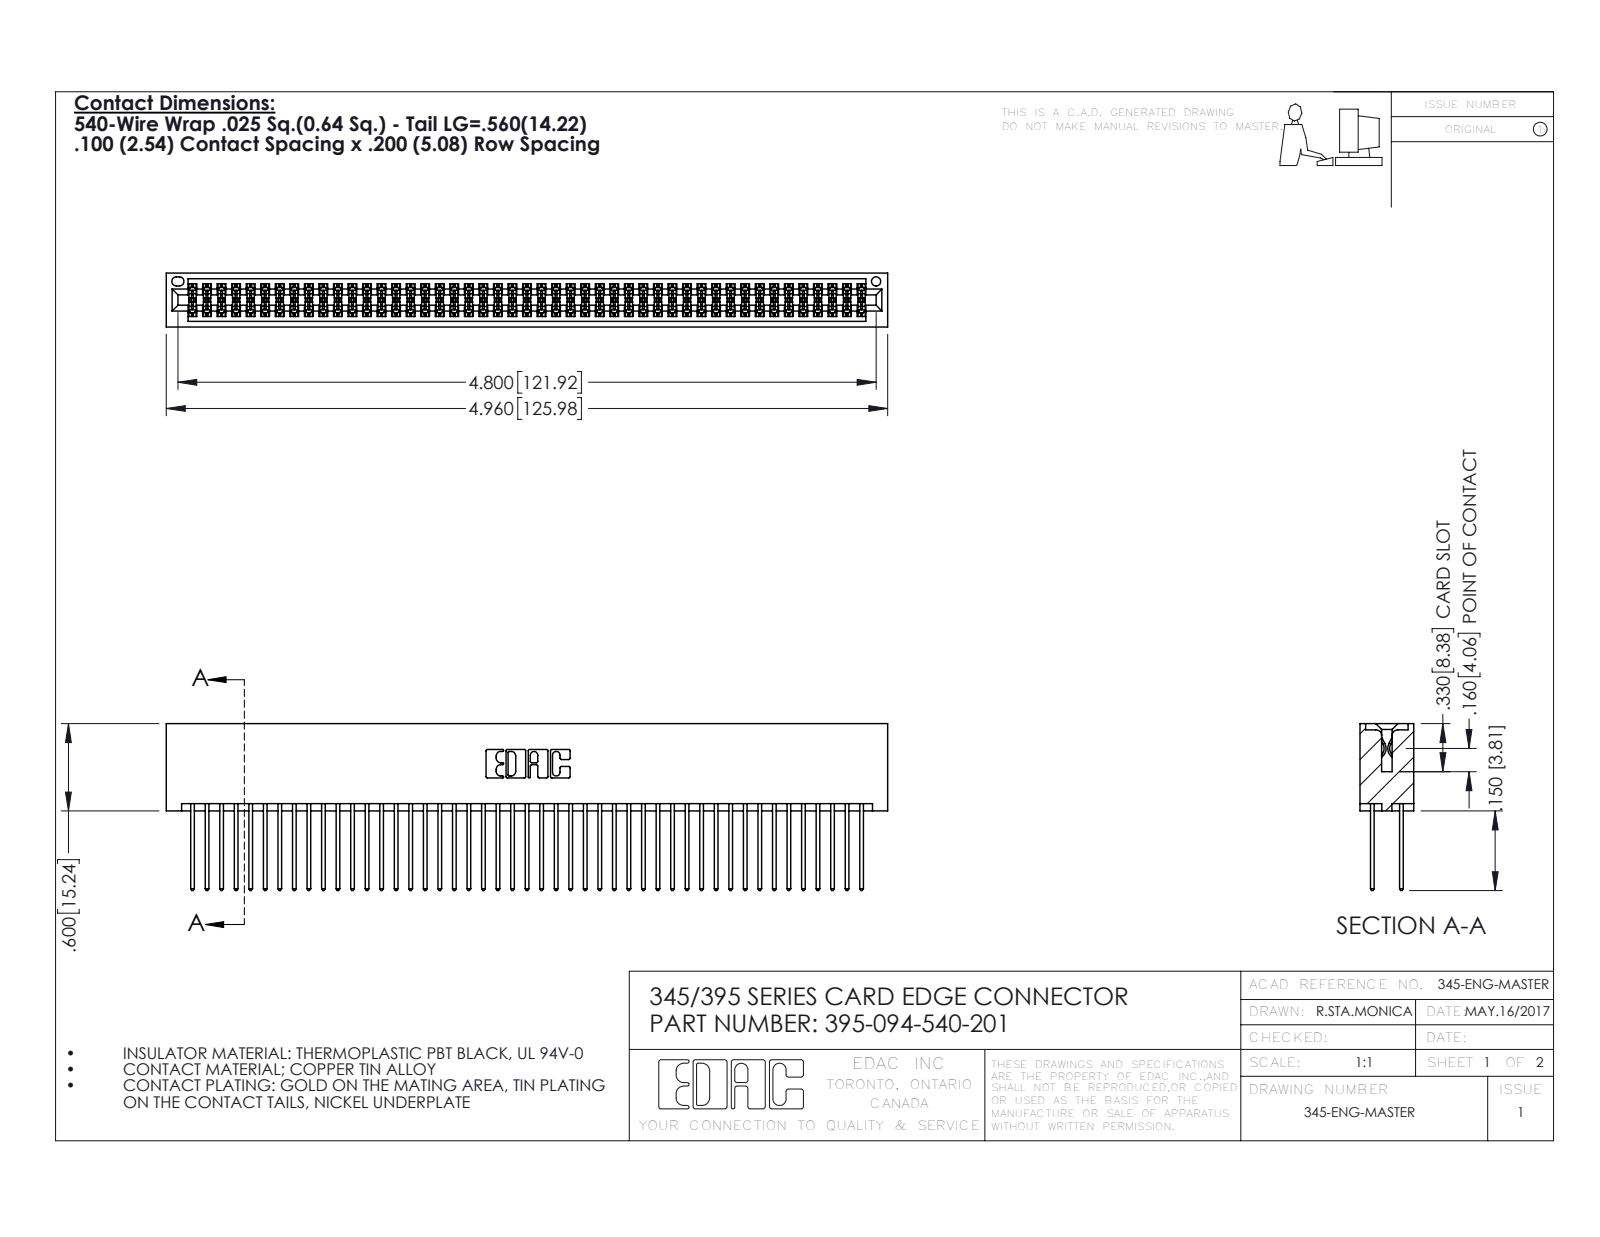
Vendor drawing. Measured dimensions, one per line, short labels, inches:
name: 345 Part_No Mounting Lugs; 345-292-001_345-293-140; 395-094-540-201
written by: SolidWorks 2016 (CONFIG_CONTROL_DESIGN)
unit: in
bodies: 95 solids, 4818 faces (3178 planar, 1640 cylindrical, 0 other)
size: 4.96 × 1.147 × 0.37
volume: 0.809 in³; area: 33.56 in²
holes: 1× ⌀0.064
rounds: 141× R0.006, 94× R0.01, 22× R0.01, 6× R0.007, 6× R0.031, 3× R0.026, 2× R0.014, 2× R0.019
face distances: 0.298, 0.072, 0.2, 0.098, 0.272, 0.025, 0.225, 0.37, 0.175, 0.149
